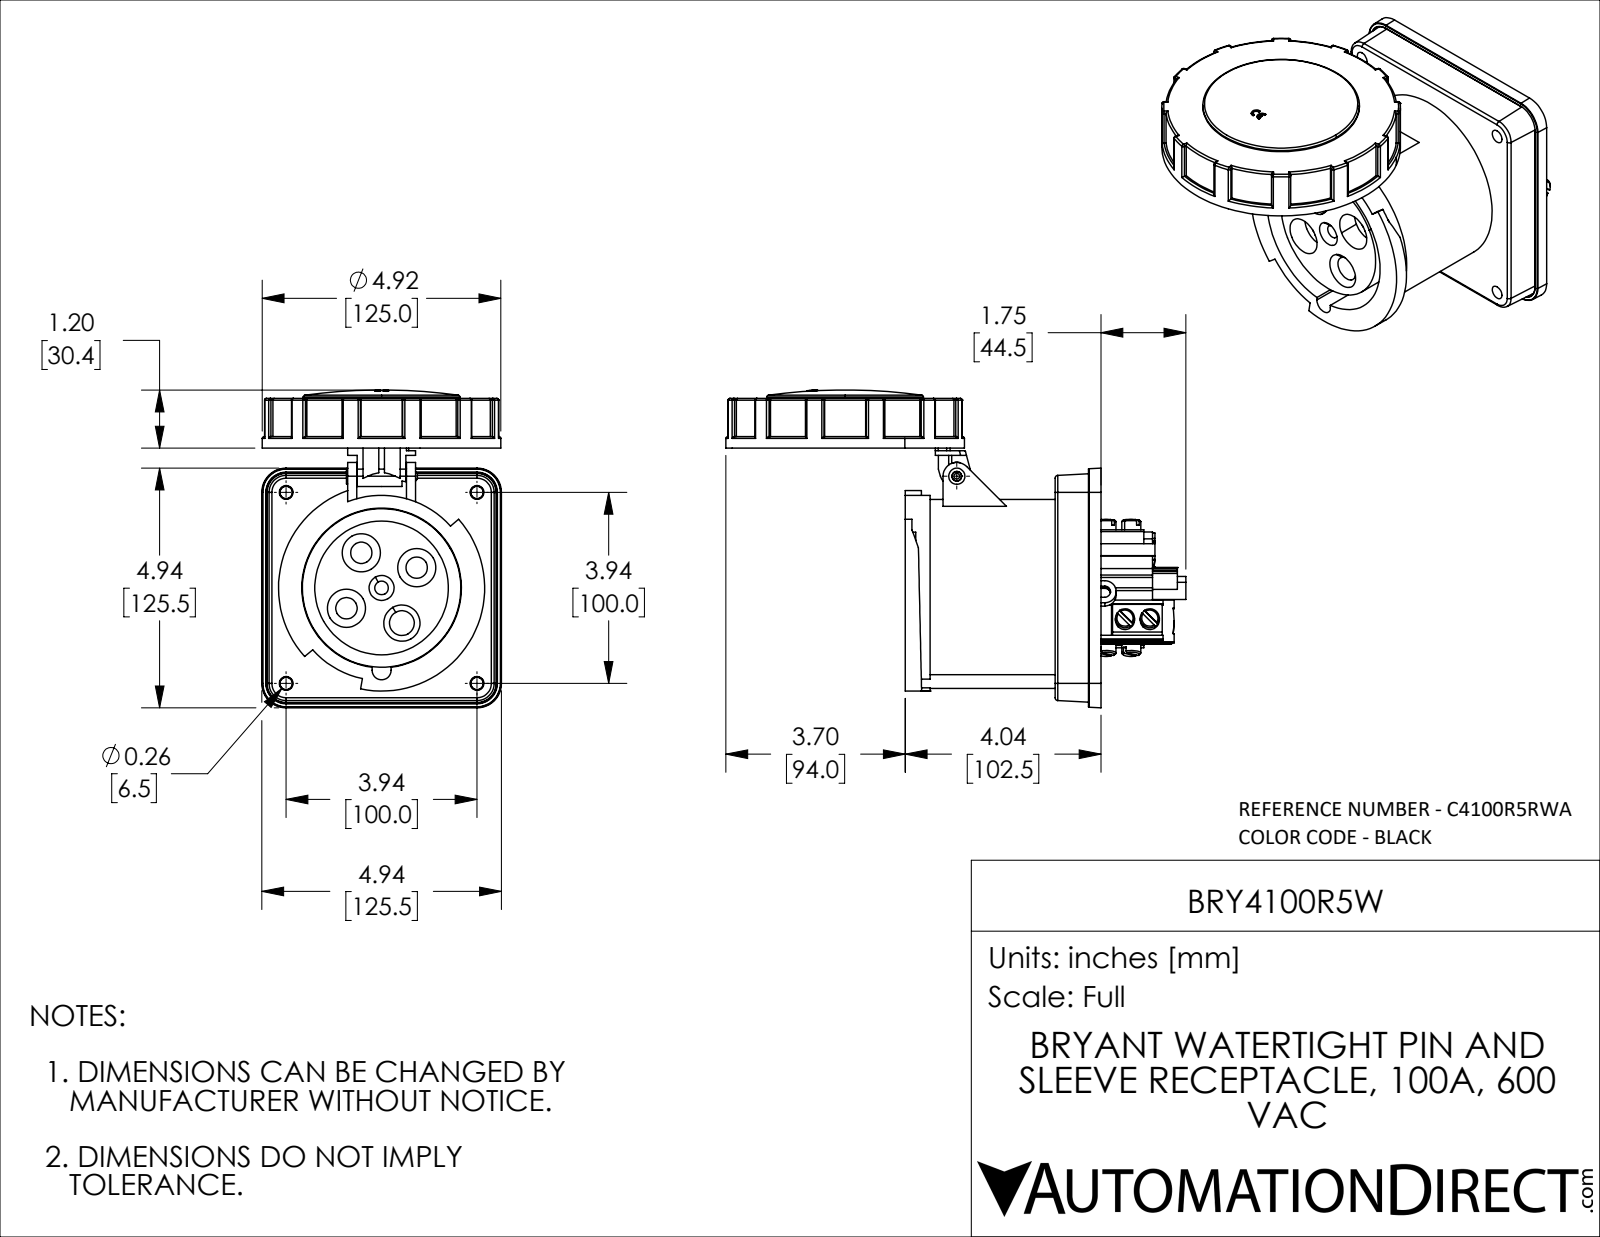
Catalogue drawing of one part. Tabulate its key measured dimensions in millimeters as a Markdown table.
| quantity | value |
| --- | --- |
| part name | BRY4100R5W |
| STEP written by | SolidWorks 2021 (CONFIG_CONTROL_DESIGN) |
| units | millimeters |
| bodies | 2 solids, 974 faces (448 planar, 361 cylindrical, 165 other) |
| overall size | 241 × 166.4 × 125.5 |
| volume | 1 113 000 mm³ |
| surface area | 180 652 mm² |
| round holes (diameter × count) | 7.2 × 4, 11.2 × 3, 20 × 3, 5.1 × 1, 7.1 × 1, 8.5 × 1, 13 × 1, 83 × 1, 83.6 × 1, 84 × 1, 85 × 1, 115 × 1 |
| round bosses / shafts (diameter × count) | 10 × 8, 125 × 1, 97 × 1, 92.6 × 1, 82 × 1, 80.5 × 1, 70 × 1, 12 × 1 |
| partial cylindrical surfaces (radius × count) | 1 × 55, 2 × 18, 2.5 × 10, 0.25 × 8, 3 × 6, 5 × 6, 0.5 × 5, 1.5 × 4 |
| main face-to-face distances | 24, 23, 26, 3, 3.5, 102.5, 78.5, 4, 20, 99 |
| hole center spacings | 21.24, 30.04, 50.49, 68.36, 70.71, 78.93, 91.4, 100 |
